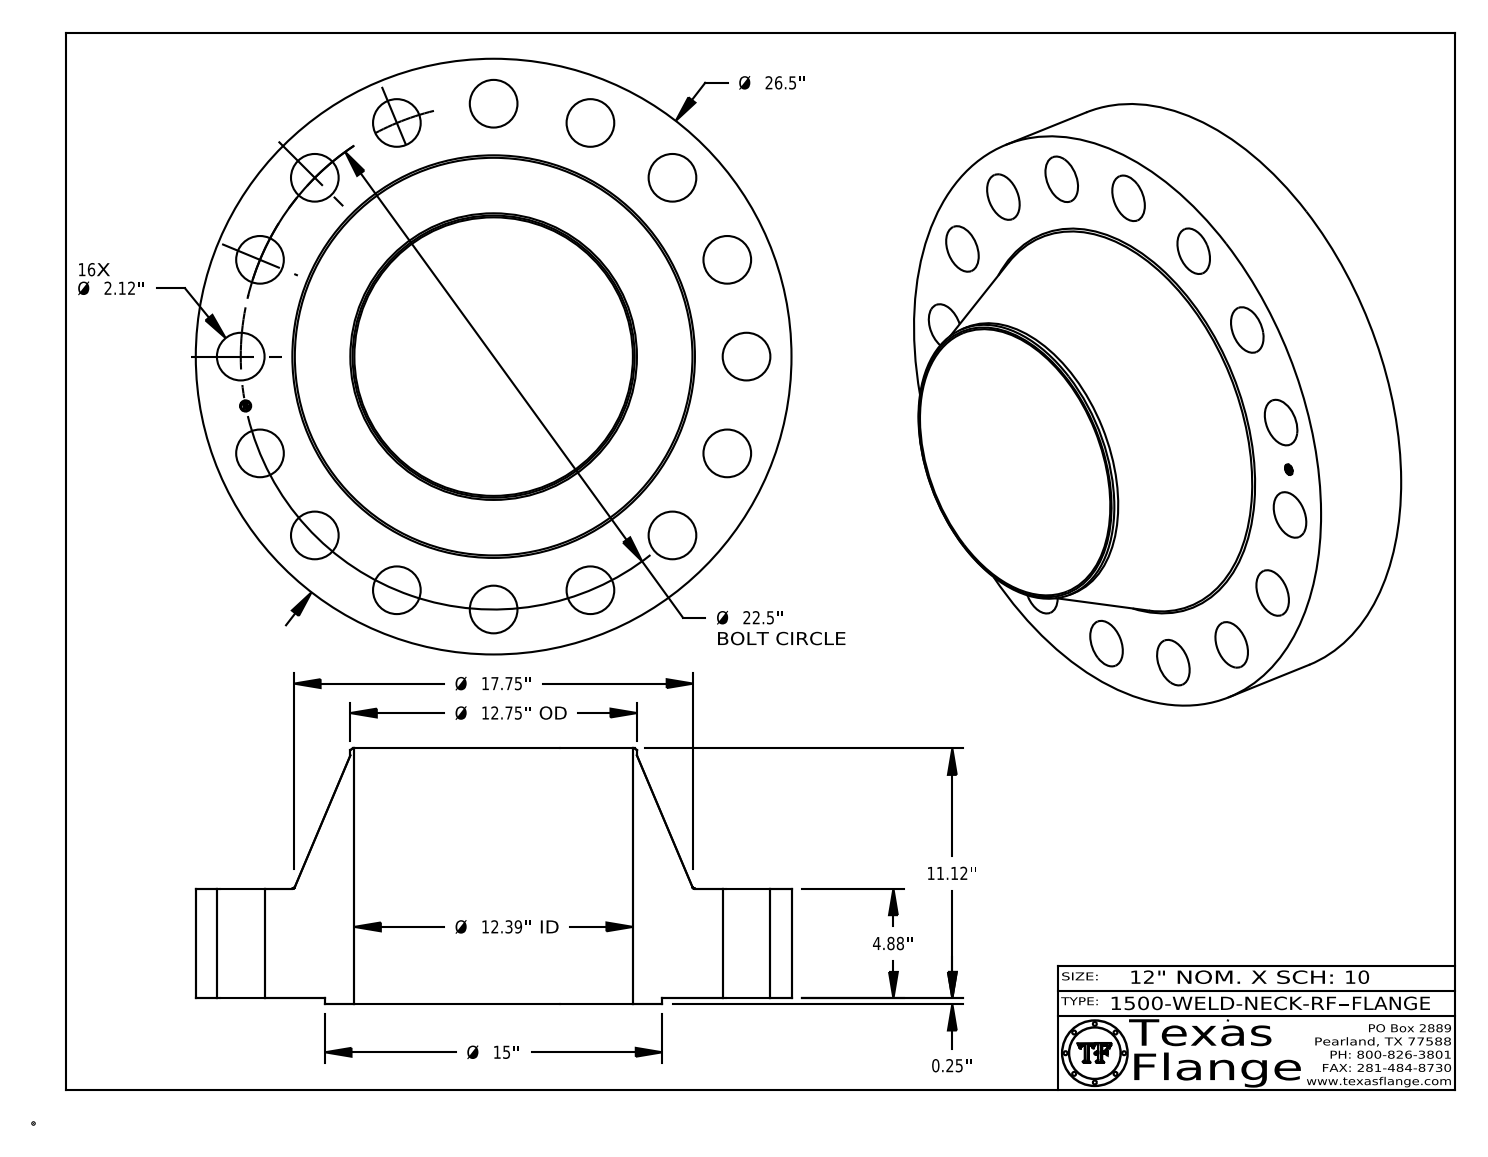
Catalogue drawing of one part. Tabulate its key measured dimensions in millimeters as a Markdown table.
| quantity | value |
| --- | --- |
| part name | 1500-WELD-NECK-RF |
| STEP written by | CATIA V5 STEP AP214 (AUTOMOTIVE_DESIGN) |
| units | millimeters |
| bodies | 1 solid, 435 faces (369 planar, 60 cylindrical, 6 other) |
| overall size | 673.1 × 673.1 × 288.8 |
| volume | 36 400 000 mm³ |
| surface area | 1 502 000 mm² |
| round holes (diameter × count) | 53.8 × 16, 12.6 × 1, 314.7 × 1 |
| round bosses / shafts (diameter × count) | 0.8 × 8, 673.1 × 1, 381 × 1, 323.9 × 1, 9.9 × 1 |
| main face-to-face distances | 124, 6.4, 130.3, 288.8, 282.4, 158.5, 129.9, 123.6, 0.4, 158.9 |
| hole center spacings | 317.5, 528, 560.5, 285.8, 218.7, 404.1, 111.5, 111.5 |
